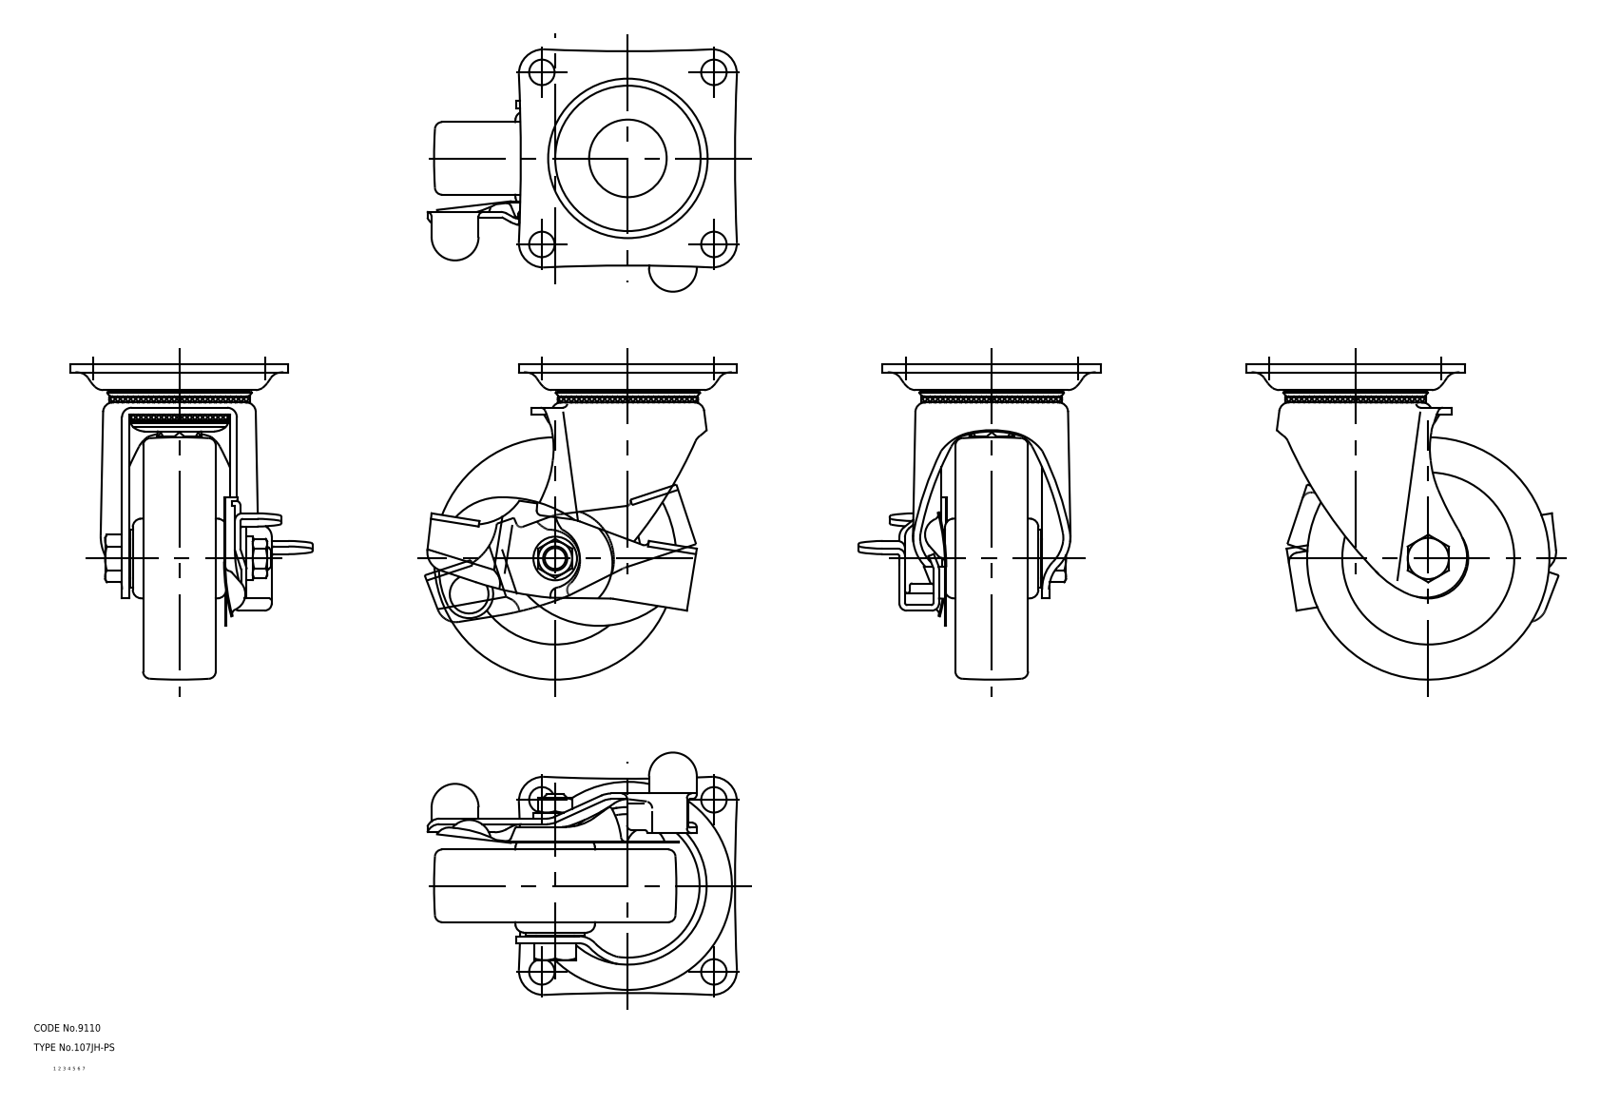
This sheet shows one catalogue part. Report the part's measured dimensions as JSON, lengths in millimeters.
{"part_name": "67147257; 67147270; 67147283; 67147296 (+8 more)", "step_written_by": "CADfix (AUTOMOTIVE_DESIGN)", "units": "millimeters", "bodies": {"solids": 6, "faces": 519, "planar": 0, "cylindrical": 0, "other": 519}, "overall_size": [130, 127.77, 100.61], "volume_mm3": 317844, "surface_area_mm2": 104785}
